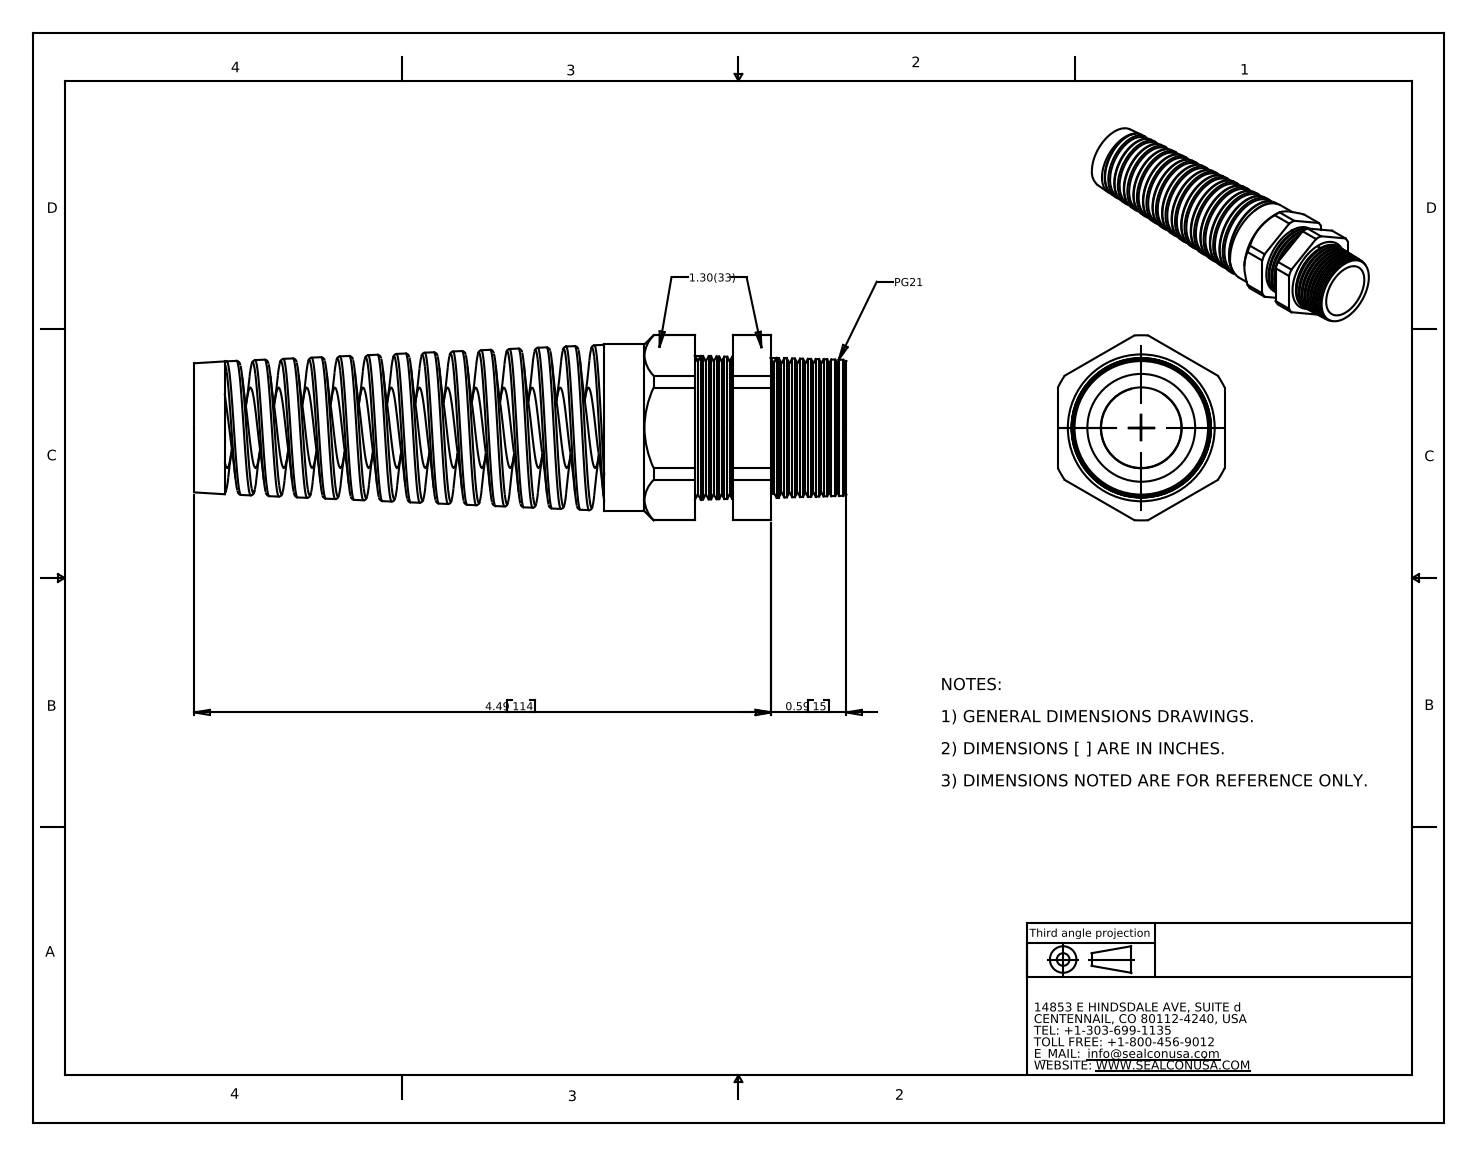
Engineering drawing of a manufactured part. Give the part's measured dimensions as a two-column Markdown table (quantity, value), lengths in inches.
| quantity | value |
| --- | --- |
| part name | CF21CR-GY |
| STEP written by | SolidWorks 2007 (CONFIG_CONTROL_DESIGN) |
| units | inches |
| bodies | 2 solids, 216 faces (24 planar, 53 cylindrical, 139 other) |
| overall size | 5.08 × 1.443 × 1.3 |
| volume | 2.956 in³ |
| surface area | 48.5 in² |
| round holes (diameter × count) | 0.626 × 1, 0.63 × 1, 0.655 × 1 |
| round bosses / shafts (diameter × count) | 1.3 × 1, 0.84 × 1 |
| partial cylindrical surfaces (radius × count) | 0.721 × 1 |
| main face-to-face distances | 1.3, 0.295, 3.9, 4.195, 4.491, 0.59, 0.295, 3.193, 0.707, 1.002 |
